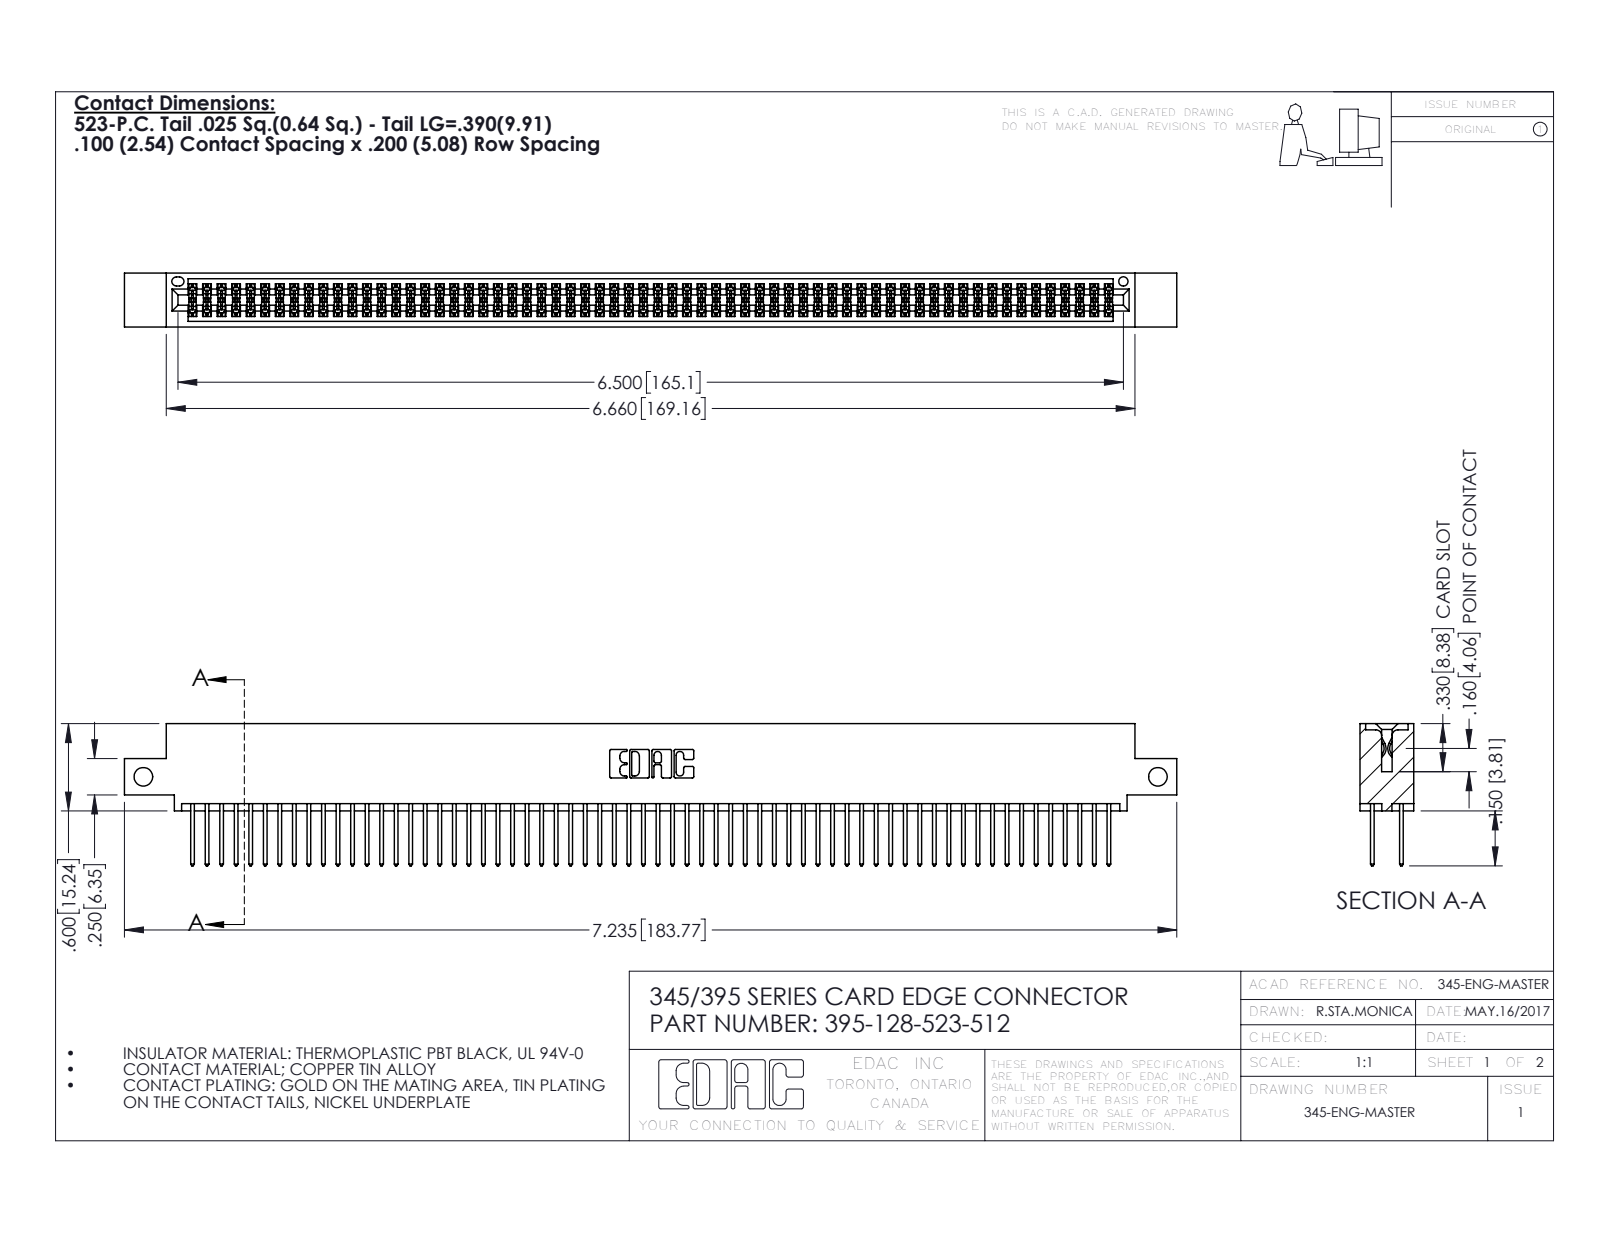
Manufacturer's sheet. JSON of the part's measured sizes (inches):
{"part_name": "345 Part_0.110 Offset - Side Mount; 395-128-523-512; 345-292-001_345-293-123", "step_written_by": "SolidWorks 2016 (CONFIG_CONTROL_DESIGN)", "units": "inches", "bodies": {"solids": 129, "faces": 6530, "planar": 4308, "cylindrical": 2222, "other": 0}, "overall_size": [7.235, 0.977, 0.37], "volume_in3": 1.108, "surface_area_in2": 44.02, "round_holes": [[0.128, 2], [0.064, 1]], "partial_cylinders_radius": [[0.006, 192], [0.01, 128], [0.01, 22], [0.007, 6], [0.031, 6], [0.026, 3], [0.014, 2], [0.019, 2]], "face_to_face_distances": [0.298, 0.072, 0.2, 0.098, 0.272, 0.025, 0.37, 0.225, 0.175, 0.149], "hole_center_spacings": [6.975]}
